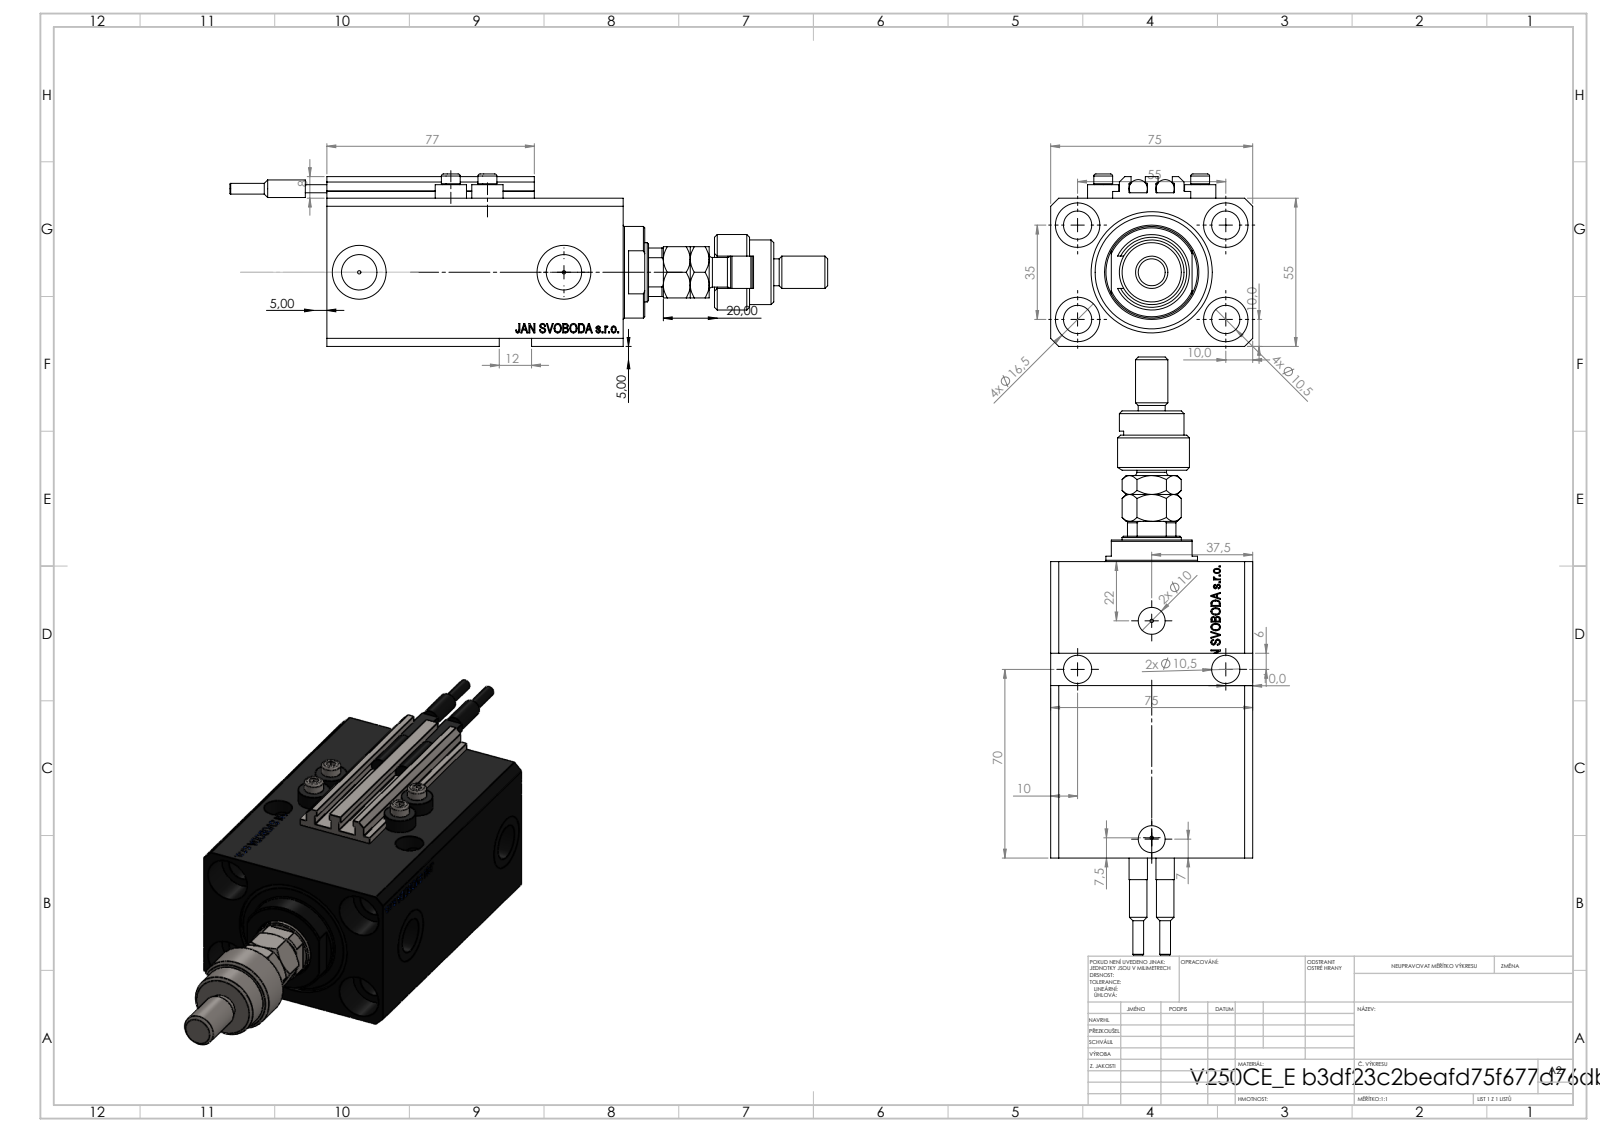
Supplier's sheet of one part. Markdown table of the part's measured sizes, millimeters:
| quantity | value |
| --- | --- |
| part name | V250CE_E_Body; V250CE_VC_E; SWITCH_V250CE; MFA (+3 more) |
| STEP written by | SolidWorks 2019 (CONFIG_CONTROL_DESIGN) |
| units | millimeters |
| bodies | 12 solids, 1237 faces (578 planar, 183 cylindrical, 476 other) |
| overall size | 222 × 75 × 64 |
| volume | 399 171 mm³ |
| surface area | 106 662 mm² |
| round holes (diameter × count) | 10.5 × 9, 1.25 × 4, 4 × 4, 16.5 × 4, 10 × 2, 13.16 × 2, 20 × 2, 22 × 1, 32 × 1, 45 × 1 |
| round bosses / shafts (diameter × count) | 11.6 × 4, 7 × 4, 6.8 × 2, 6.5 × 2, 4 × 2, 34 × 1, 28 × 1, 24 × 1 |
| partial cylindrical surfaces (radius × count) | 0.2 × 10, 9.75 × 1, 10.5 × 1 |
| main face-to-face distances | 55, 75, 15, 3, 110, 57, 95, 9.9, 8, 19 |
| hole center spacings | 32.6, 32.87, 55, 68.74, 13.6, 14.09, 23.05, 25.81 |
